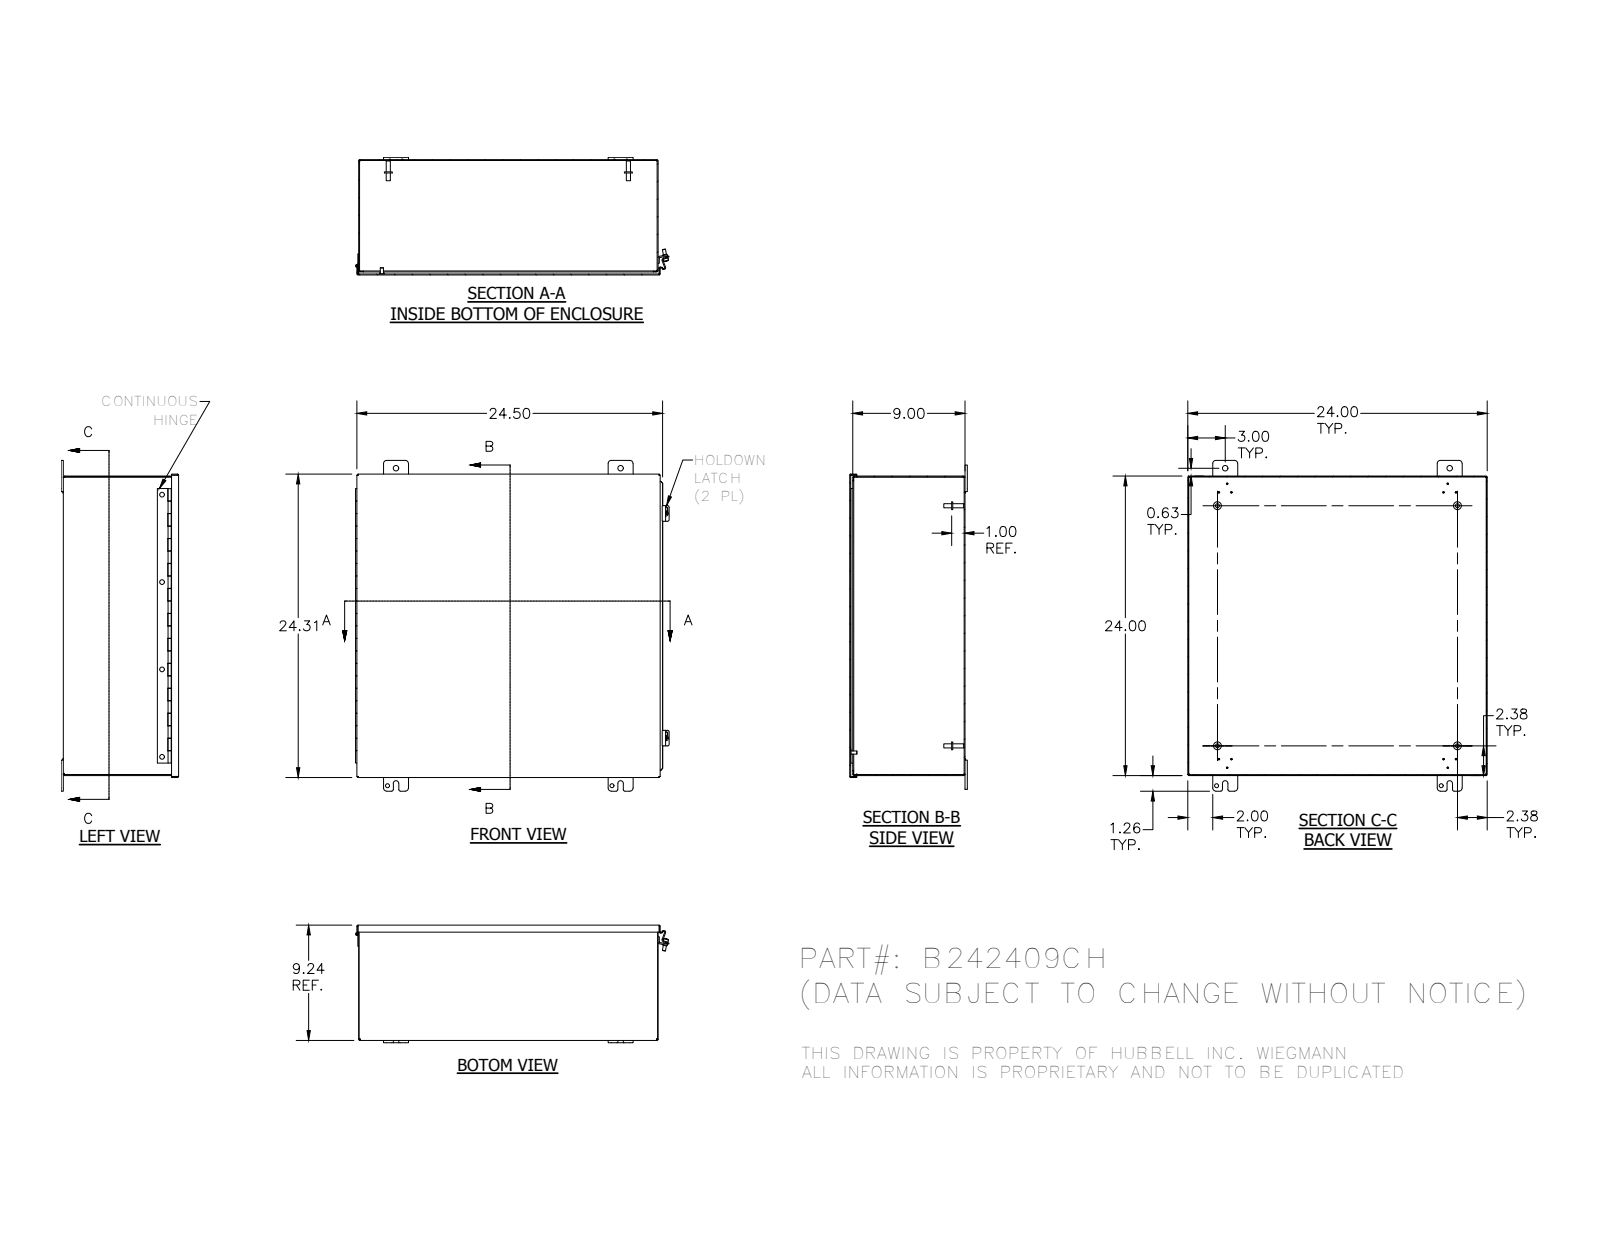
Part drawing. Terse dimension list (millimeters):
name: B242409CH; B242409CHBKP; B2424CHLID; H6010101 (+8 more)
written by: Autodesk Inventor 2012 (AUTOMOTIVE_DESIGN)
unit: mm
bodies: 20 solids, 649 faces (395 planar, 185 cylindrical, 69 other)
size: 673.2 × 638.5 × 239.3
volume: 2 658 000 mm³; area: 2 824 000 mm²
holes: 4× ⌀2.8, 4× ⌀8, 4× ⌀9.5, 4× ⌀11.1, 2× ⌀5, 1× ⌀3.2, 1× ⌀3.2
bosses: 4× ⌀15.9, 4× ⌀8.4, 4× ⌀6.4, 2× ⌀10.4, 2× ⌀8.7, 1× ⌀8.6, 1× ⌀3
rounds: 16× R3.2, 16× R6.4, 8× R0.8, 8× R1.6, 8× R1.8, 8× R2.7, 5× R0.4, 5× R2.3
face distances: 1.9, 232.9, 607.7, 234.8, 231, 609.6, 605.8, 3.5, 611.2, 226.7
hole spacings: 457.2, 762.1, 40.5, 177.8, 609.7, 19.1, 355.6, 441.2
